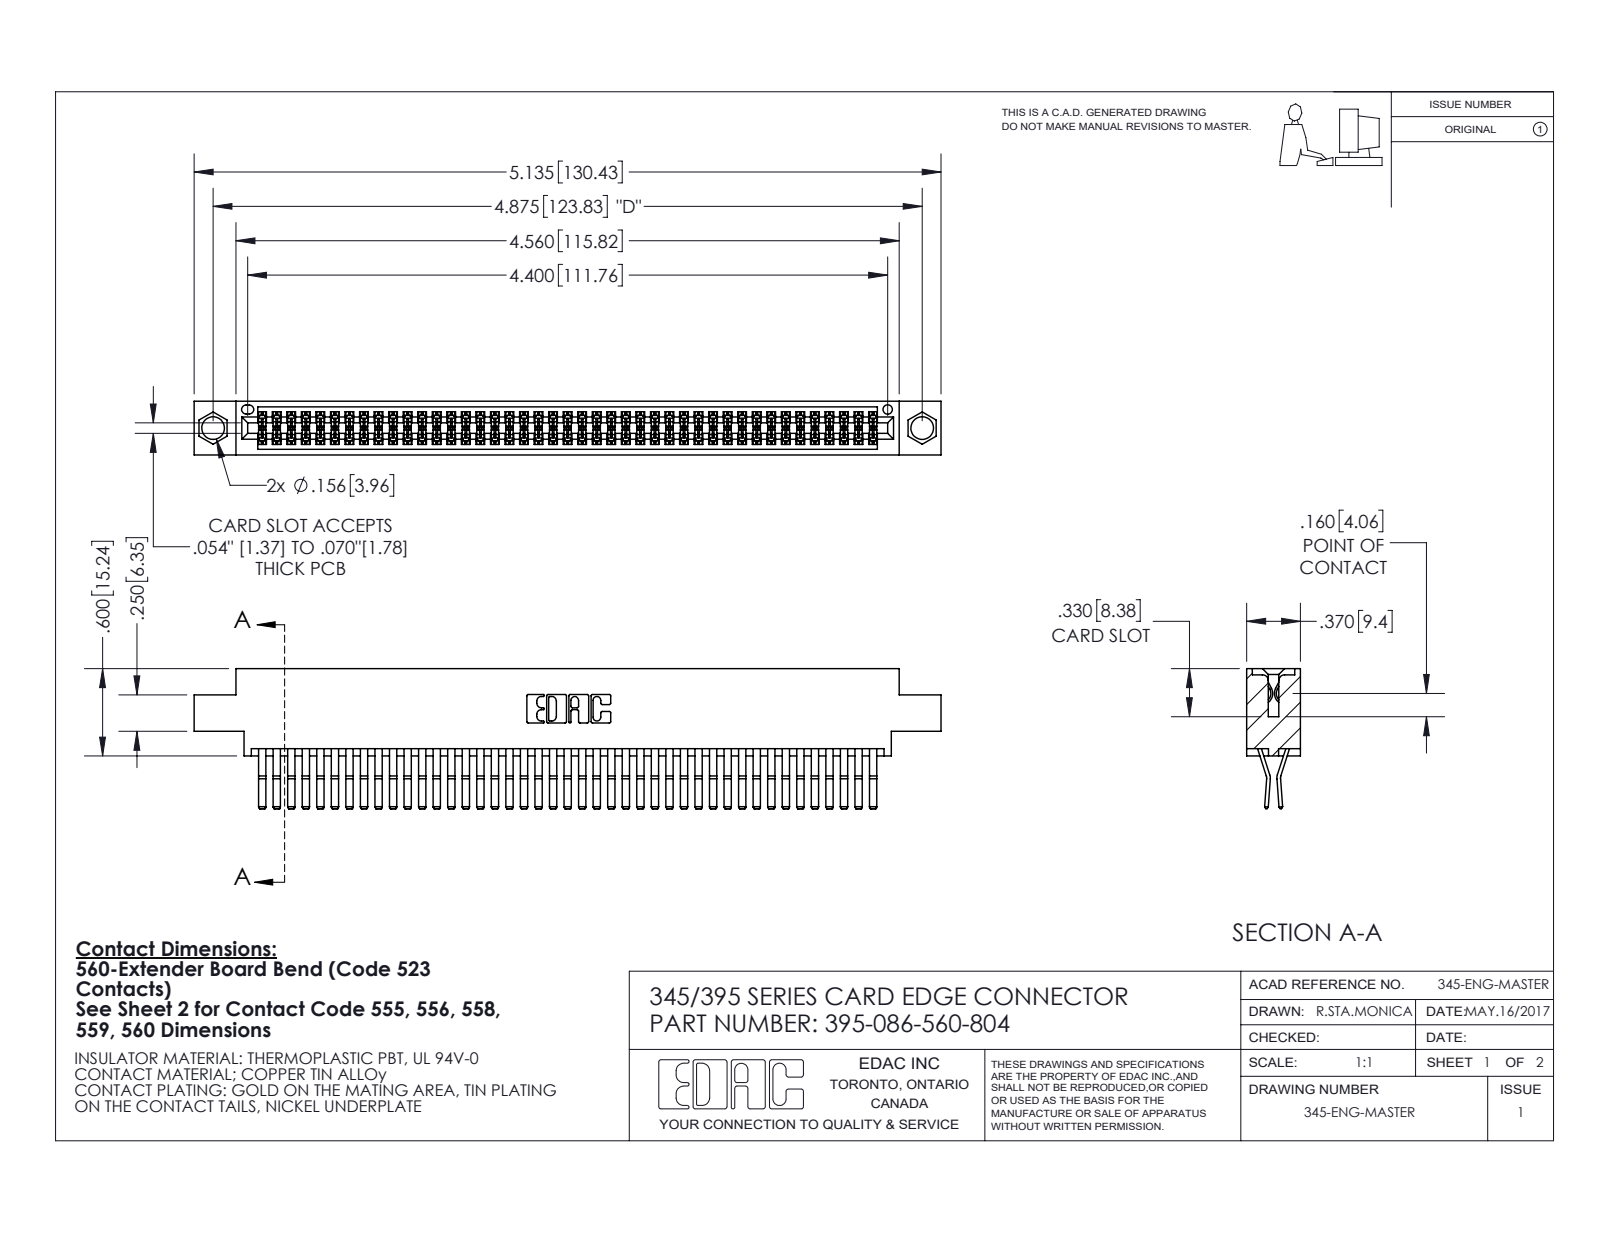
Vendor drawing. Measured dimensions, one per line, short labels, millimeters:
name: 345-292-001_560 Tail; 345 Part_0.170 Offset - 0.156 Dia-TI; 395-086-560-804
written by: SolidWorks 2020 (CONFIG_CONTROL_DESIGN)
unit: mm
bodies: 87 solids, 4616 faces (2936 planar, 1680 cylindrical, 0 other)
size: 130.4 × 24.4 × 9.4
volume: 13 000 mm³; area: 20 720 mm²
holes: 2× ⌀4, 1× ⌀1.6
rounds: 129× R0.2, 22× R0.3, 6× R0.2, 6× R0.8, 3× R0.7, 2× R0.3, 2× R0.4, 2× R0.5
face distances: 0.6, 7.6, 1.8, 9.4, 5.1, 2.5, 6.9, 5.7, 4.4, 3.8
hole spacings: 6.9, 117.8, 123.8
